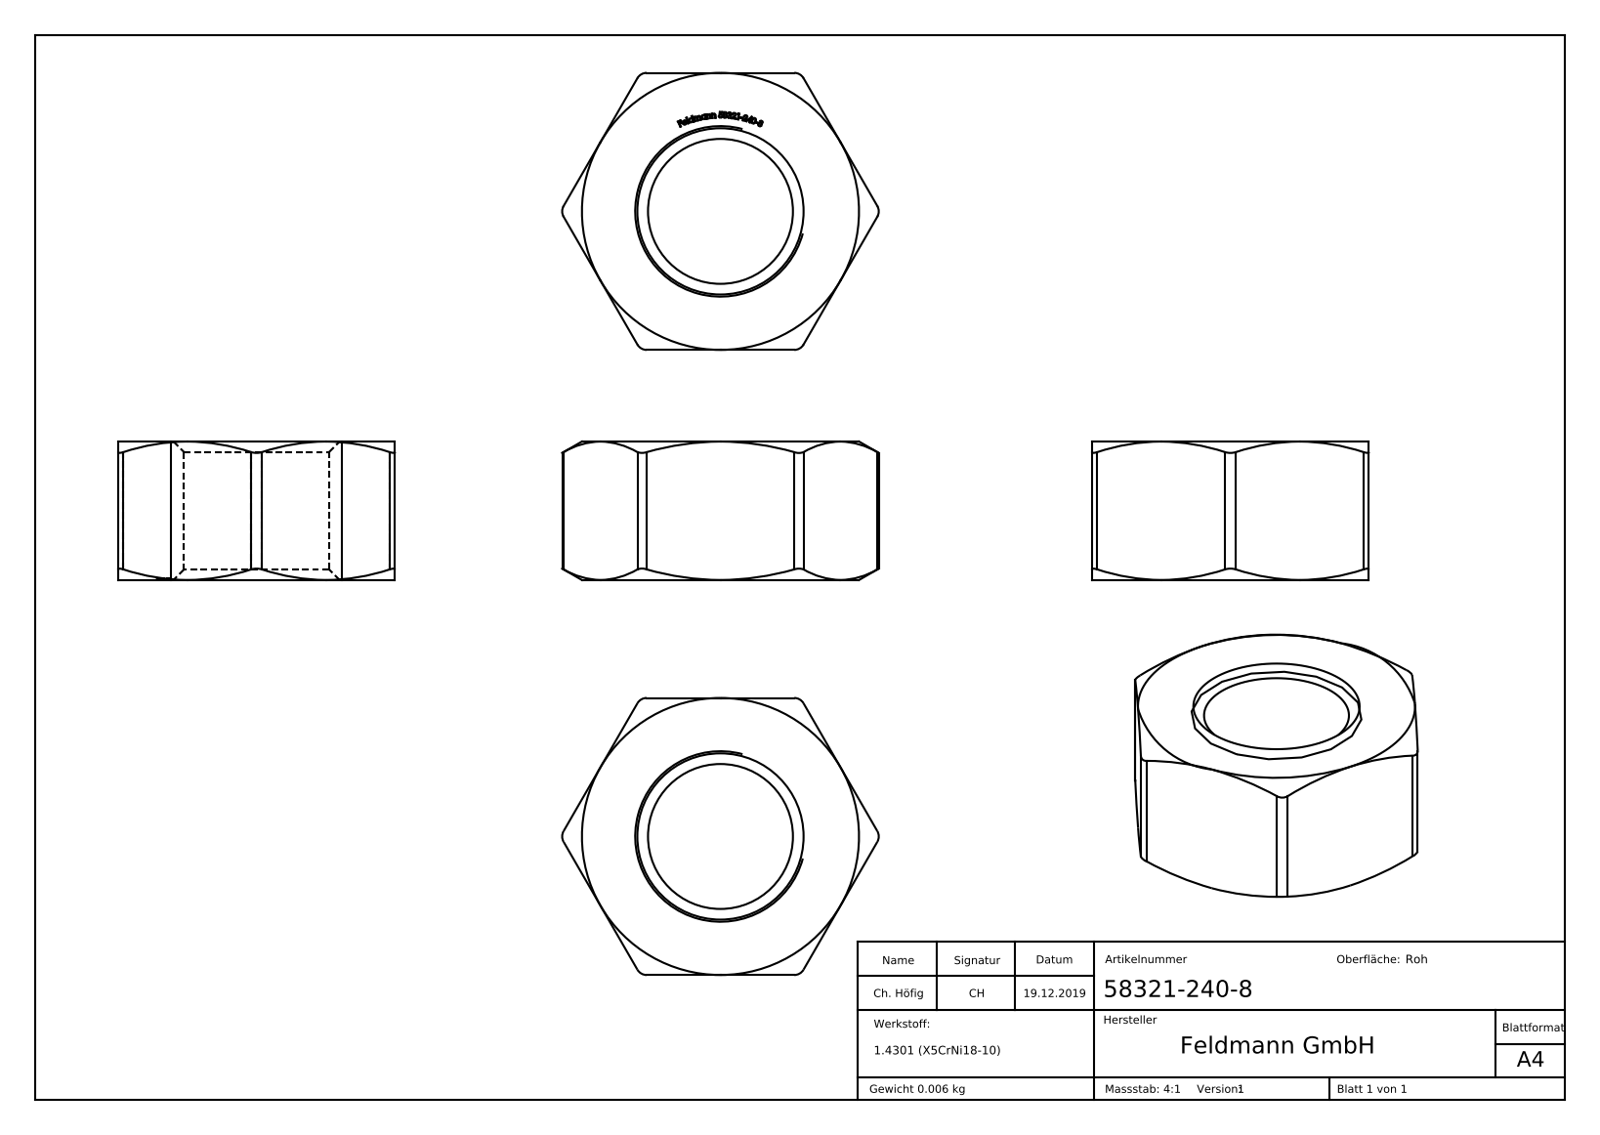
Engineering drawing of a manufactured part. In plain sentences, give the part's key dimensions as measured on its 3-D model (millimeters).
The part is named "58321-240-8". Its 3-D file was written by "SolidWorks 2015 (CONFIG_CONTROL_DESIGN)". It is 1 solid with 29 faces: 8 planar, 7 cylindrical and 14 other. Overall it measures 22 by 14.86 by 13 millimeters. Its volume is 704 cubic millimeters and its surface area 624 square millimeters. Round holes: 1 of diameter 6.8. Partial cylindrical surfaces (rounded edges, fillets, slot ends): 6 of radius 0.5. The main face-to-face distances are 13, 6.5.
